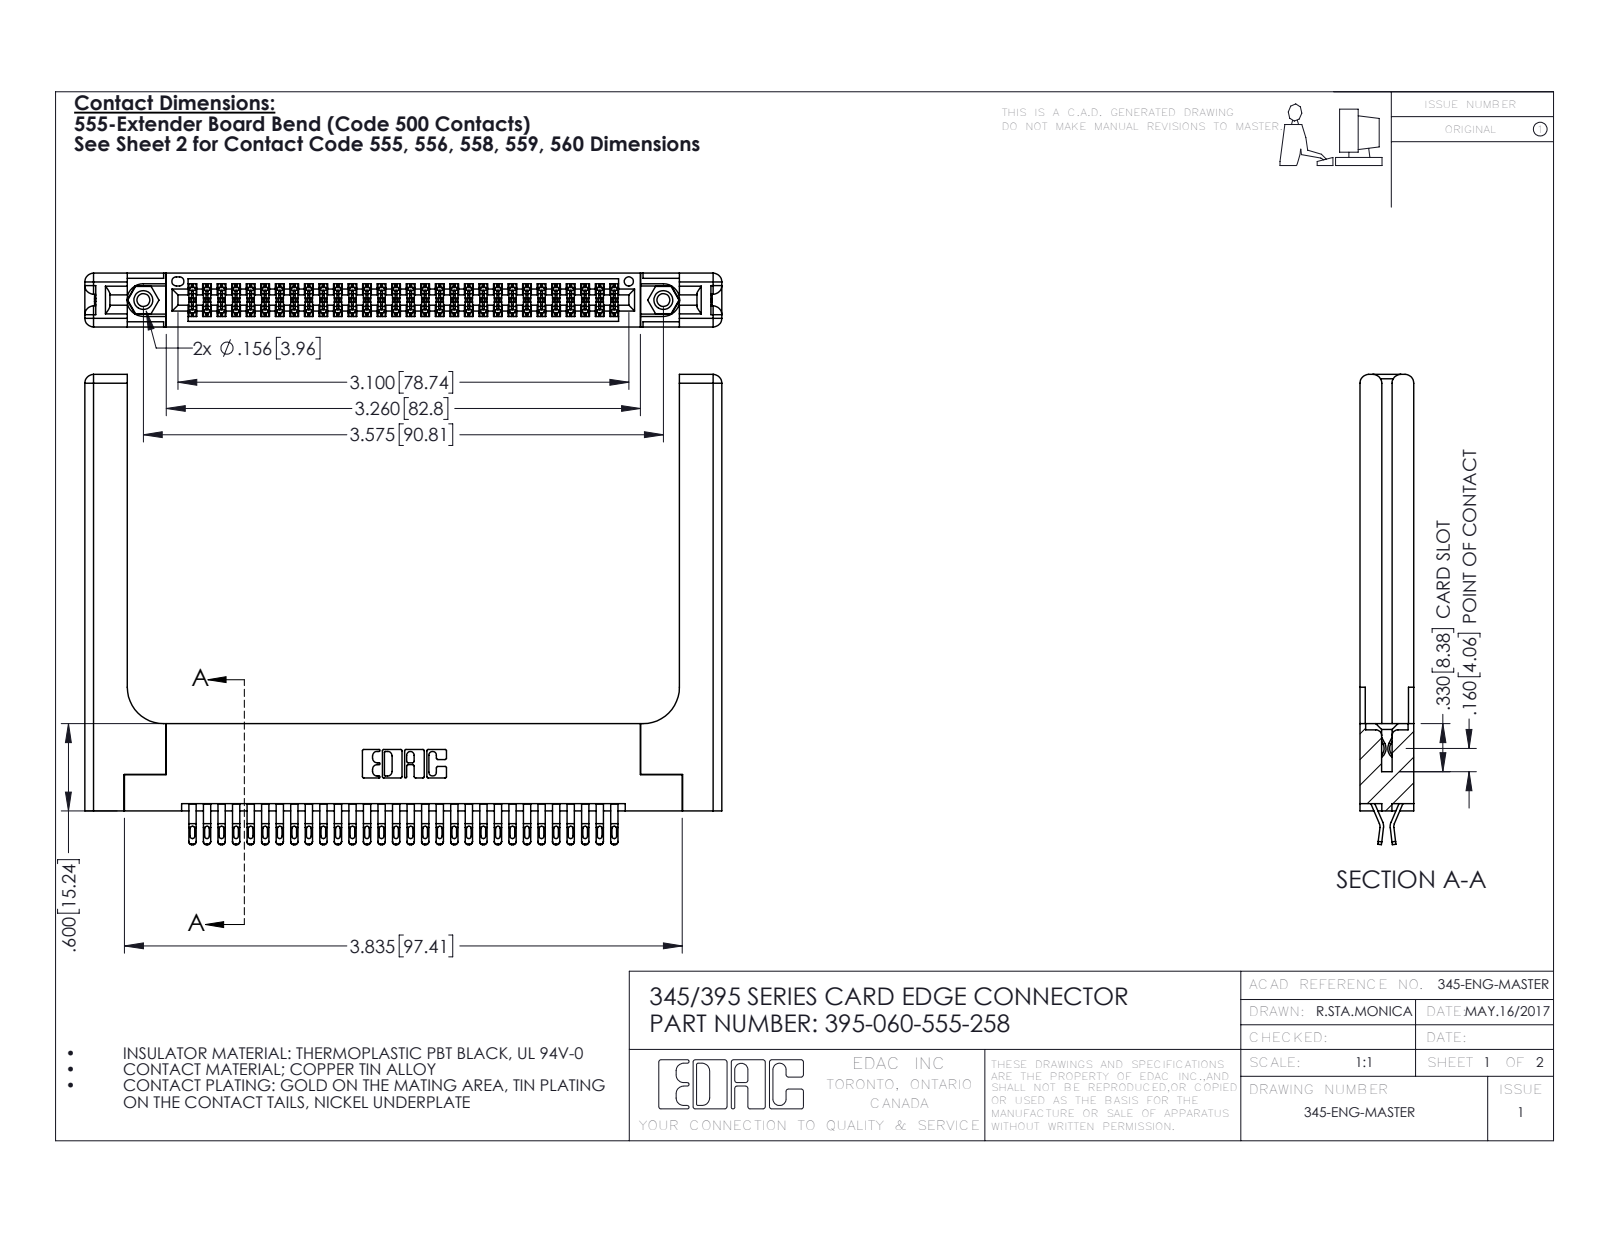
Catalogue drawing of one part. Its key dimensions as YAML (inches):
part_name: "345 Part_Flush Mounting Lugs - 0.156 Dia-TH; 395-060-555-258; 345-220-058_345-220-058; 345-292-001_555 Tail (+1 more)"
step_written_by: "SolidWorks 2016 (CONFIG_CONTROL_DESIGN)"
units: inches
bodies: {solids: 65, faces: 3742, planar: 2088, cylindrical: 1594, other: 60}
overall_size: [4.379, 3.232, 0.37]
volume: 1.18
surface_area: 33.32
round_holes:
  - {diameter: 0.089, count: 2}
  - {diameter: 0.125, count: 2}
  - {diameter: 0.156, count: 2}
  - {diameter: 0.064, count: 1}
round_bosses_or_shafts:
  - {diameter: 0.155, count: 2}
partial_cylinders:
  - {radius: 0.016, count: 150}
  - {radius: 0.02, count: 120}
  - {radius: 0.006, count: 90}
  - {radius: 0.01, count: 22}
  - {radius: 0.06, count: 16}
  - {radius: 0.007, count: 6}
  - {radius: 0.031, count: 6}
  - {radius: 0.026, count: 3}
face_to_face_distances: [0.37, 0.072, 0.298, 0.2, 0.025, 0.225, 0.098, 0.272, 0.148, 0.15]
hole_center_spacings: [0.27, 3.34, 3.575]
